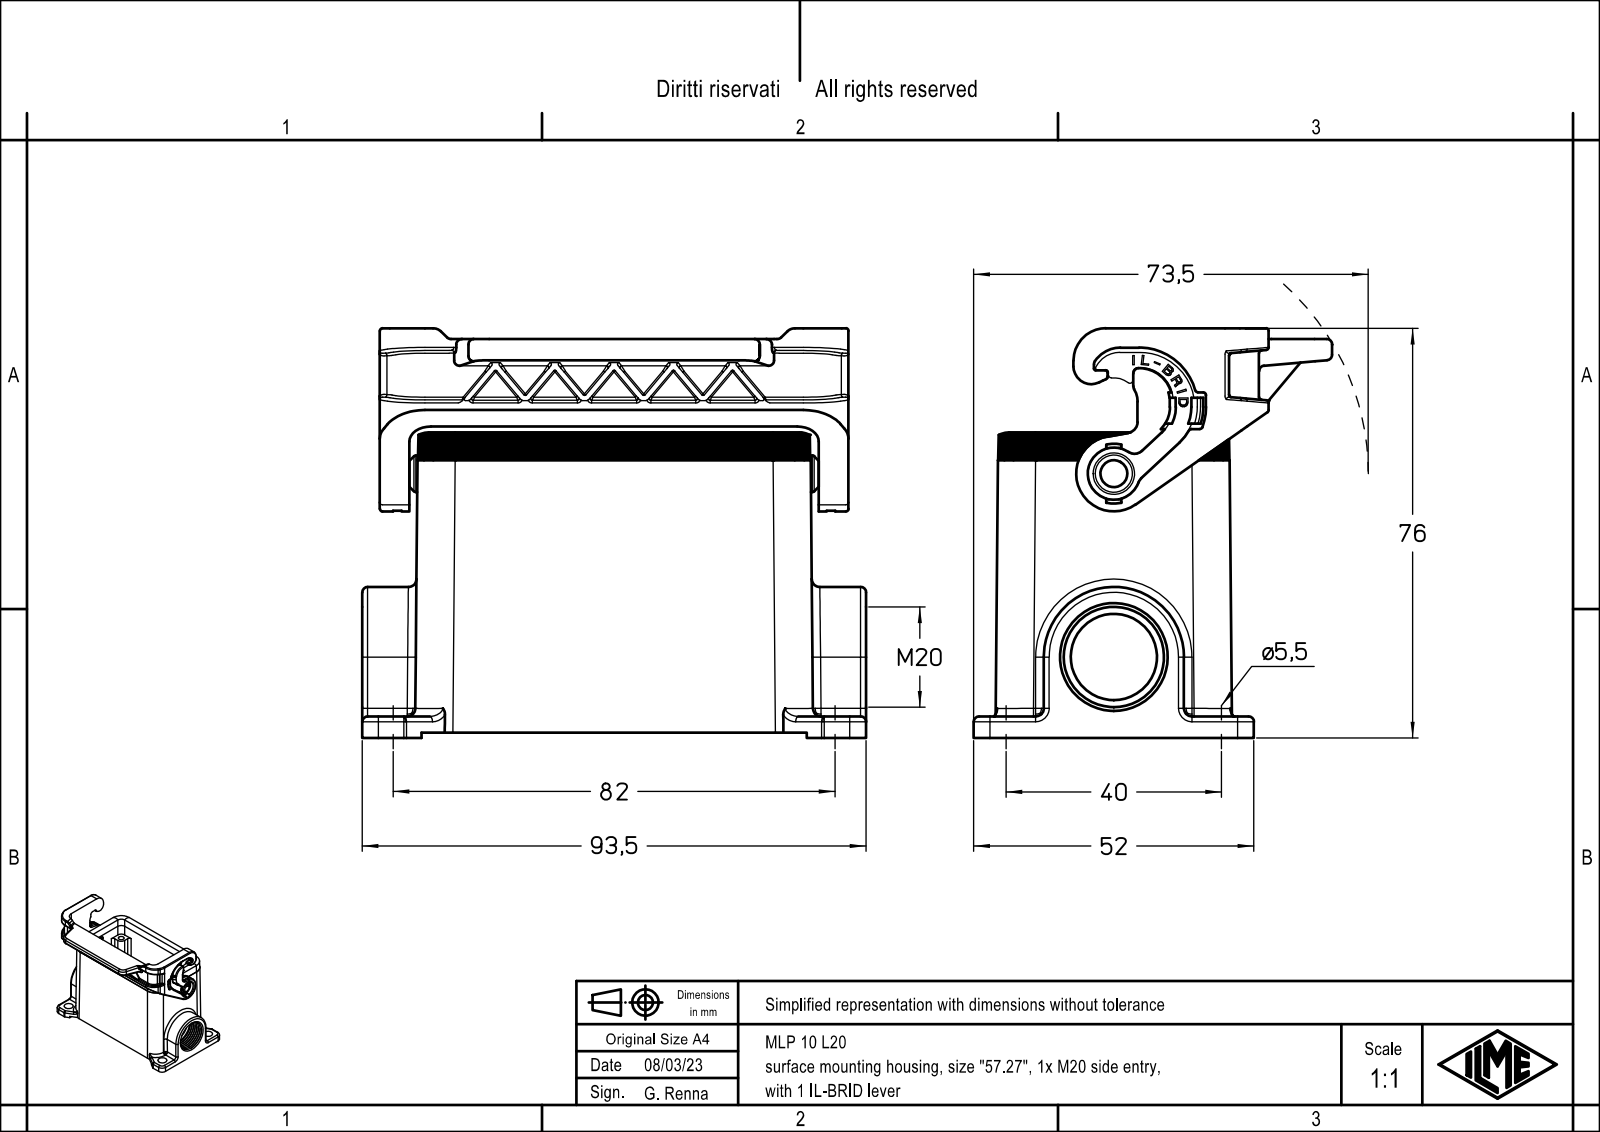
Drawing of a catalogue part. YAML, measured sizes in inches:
part_name: "MLP 10 L20"
step_written_by: "Creo Elements/Direct Modeling 20.1B 02-Apr-2019 (C) Parametric Technology GmbH (AUTOMOTIVE_DESIGN)"
units: inches
bodies: {solids: 1, faces: 1054, planar: 620, cylindrical: 304, other: 130}
overall_size: [3.681, 2.992, 2.618]
volume: 5.497
surface_area: 72.12
round_holes:
  - {diameter: 0.118, count: 4}
  - {diameter: 0.138, count: 4}
  - {diameter: 0.197, count: 4}
  - {diameter: 0.217, count: 4}
  - {diameter: 0.128, count: 1}
  - {diameter: 0.213, count: 1}
  - {diameter: 0.303, count: 1}
  - {diameter: 0.63, count: 1}
  - {diameter: 0.732, count: 1}
round_bosses_or_shafts:
  - {diameter: 0.272, count: 1}
  - {diameter: 0.268, count: 1}
  - {diameter: 0.205, count: 1}
  - {diameter: 0.126, count: 1}
partial_cylinders:
  - {radius: 0.004, count: 27}
  - {radius: 0.039, count: 18}
  - {radius: 0.059, count: 17}
  - {radius: 0.079, count: 17}
  - {radius: 0.118, count: 16}
  - {radius: 0.008, count: 15}
  - {radius: 0.02, count: 11}
  - {radius: 0.276, count: 10}
face_to_face_distances: [0.118, 0.039, 2.992, 0.157, 0.217, 3.209, 2.913, 2.874, 2.756, 1.533]
hole_center_spacings: [0.115, 0.461, 0.555, 1.163, 1.408, 1.482, 2.305, 2.58]
